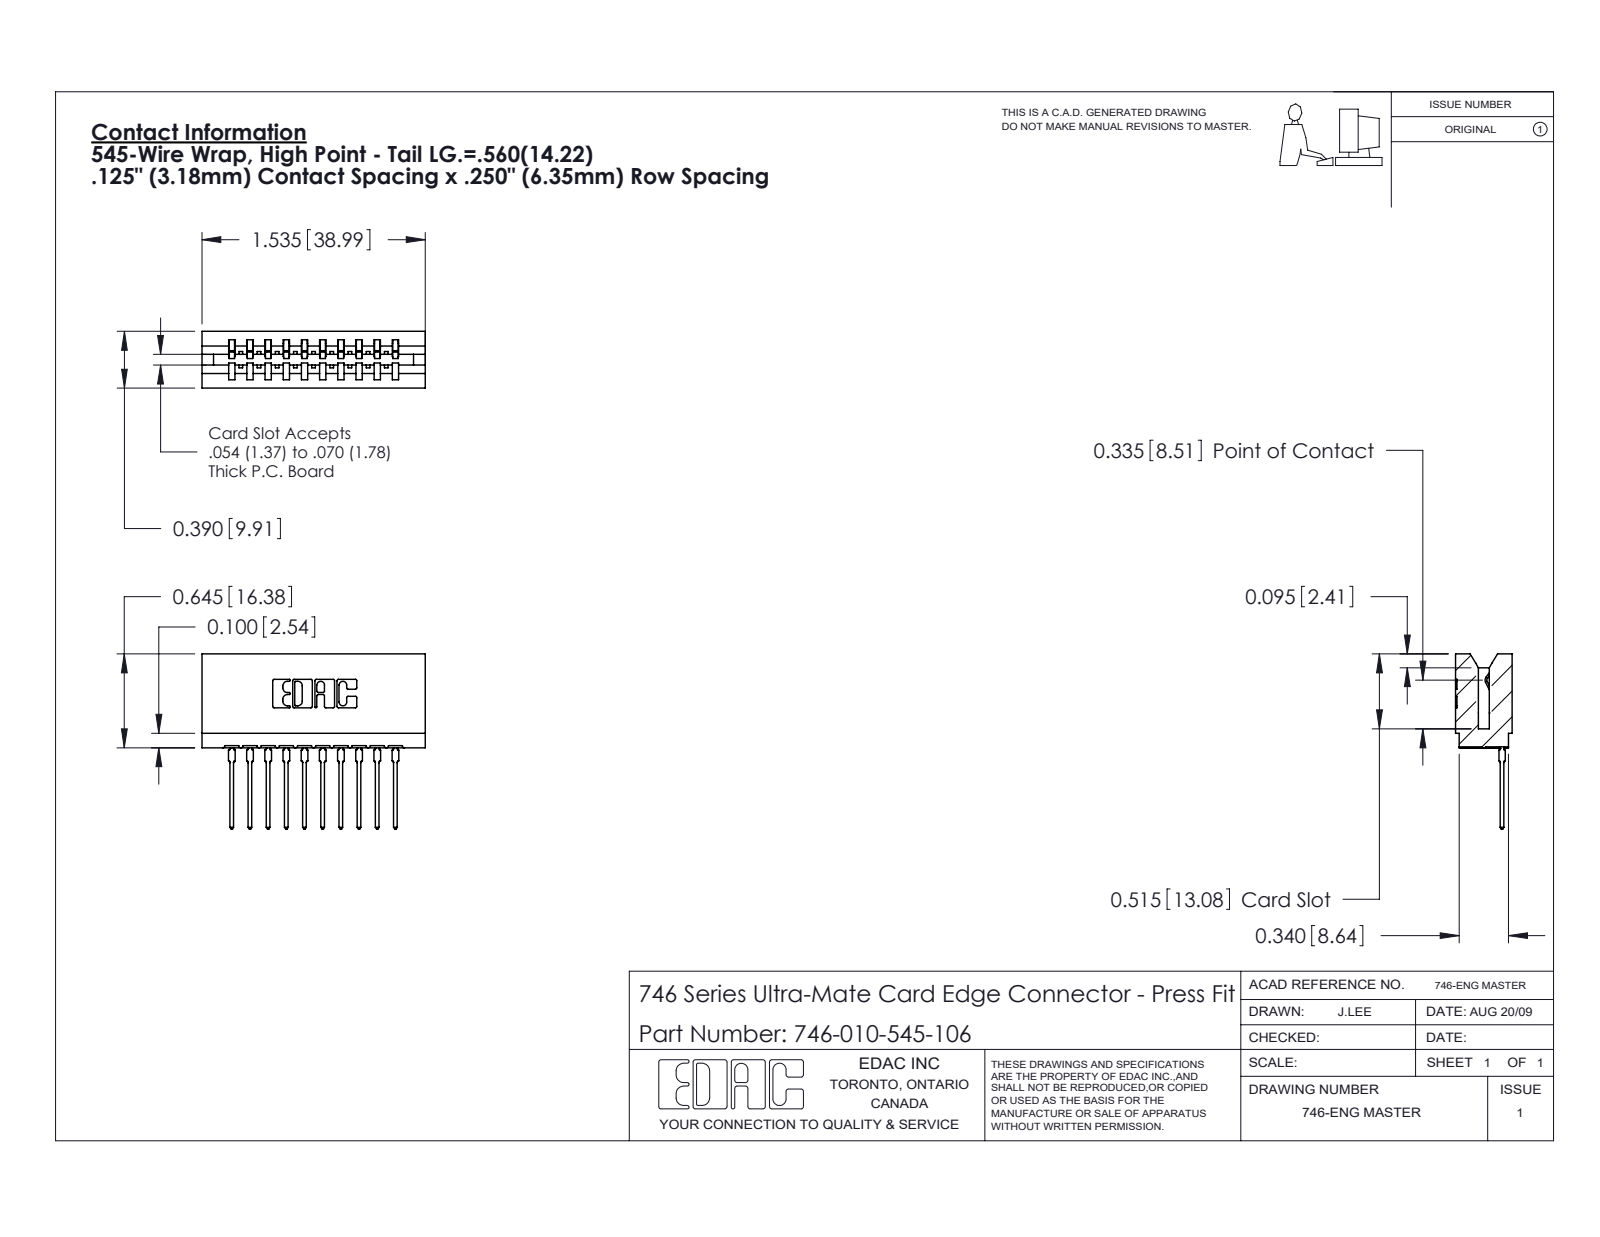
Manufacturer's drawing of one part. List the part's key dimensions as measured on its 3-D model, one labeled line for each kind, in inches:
Part name (STEP PRODUCT): 746 Part_.515 Slot Depth - 06; 746-292-001_545; 746-010-545-106
STEP written by: SolidWorks 2020 (CONFIG_CONTROL_DESIGN)
Units: inches
Bodies: 11 solids, 1178 faces (686 planar, 232 cylindrical, 260 other)
Overall size (bounding box): 1.535 × 1.204 × 0.39
Volume: 0.262 in³ · Surface area: 9.28 in²
Partial cylindrical surfaces — rounded edges, fillets, slot ends (radius × count): R0.01 ×22, R0.021 ×20, R0.015 ×11, R0.007 ×6, R0.031 ×6, R0.005 ×4, R0.011 ×4, R0.026 ×3
Main face-to-face distances: 0.25, 0.333, 0.5, 0.057, 0.042, 0.125, 0.292, 0.75, 0.39, 0.375
